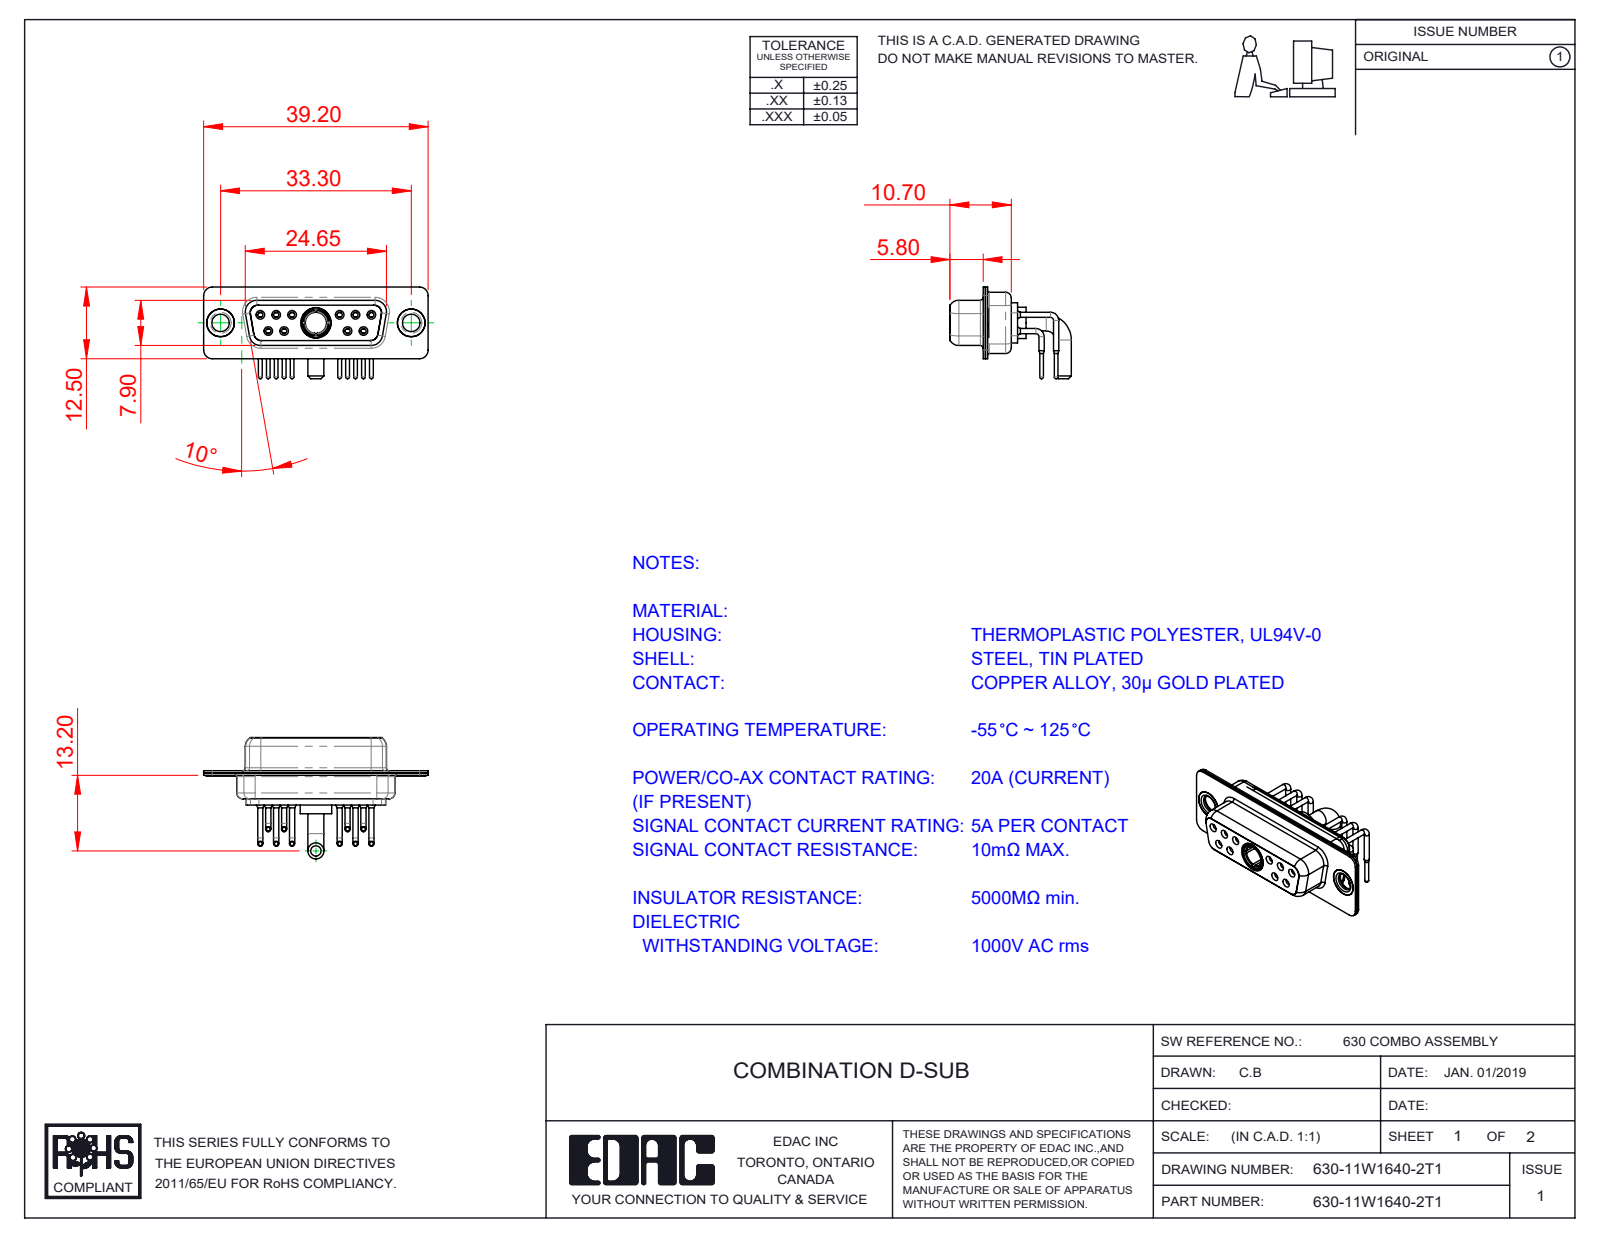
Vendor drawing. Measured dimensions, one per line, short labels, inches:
name: 630-11W1640-2T1; 630Combo Thru Hole Rivet; 630Combo Contact Row 1; Power Socket_20A RA (+4 more)
written by: SolidWorks 2020 (CONFIG_CONTROL_DESIGN)
unit: in
bodies: 17 solids, 861 faces (246 planar, 376 cylindrical, 239 other)
size: 1.543 × 0.835 × 0.63
volume: 0.157 in³; area: 9.497 in²
holes: 10× ⌀0.035, 10× ⌀0.043, 10× ⌀0.059, 10× ⌀0.079, 6× ⌀0.067, 4× ⌀0.063, 3× ⌀0.191, 2× ⌀0.12, 2× ⌀0.157, 2× ⌀0.159, 1× ⌀0.146, 1× ⌀0.209
bosses: 10× ⌀0.035, 10× ⌀0.026, 6× ⌀0.063, 2× ⌀0.197, 2× ⌀0.195, 2× ⌀0.189, 2× ⌀0.14, 2× ⌀0.11
rounds: 16× R0.059, 12× R0.053, 12× R0.079, 8× R0.063, 4× R0.01, 4× R0.02, 4× R0.024, 4× R0.026
face distances: 0.016, 0.055, 0.018, 0.333, 0.071, 0.35, 0.244, 0.031, 0.278, 0.073
hole spacings: 0.124, 0.109, 0.545, 0.436, 0.654, 0.198, 0.198, 0.218
